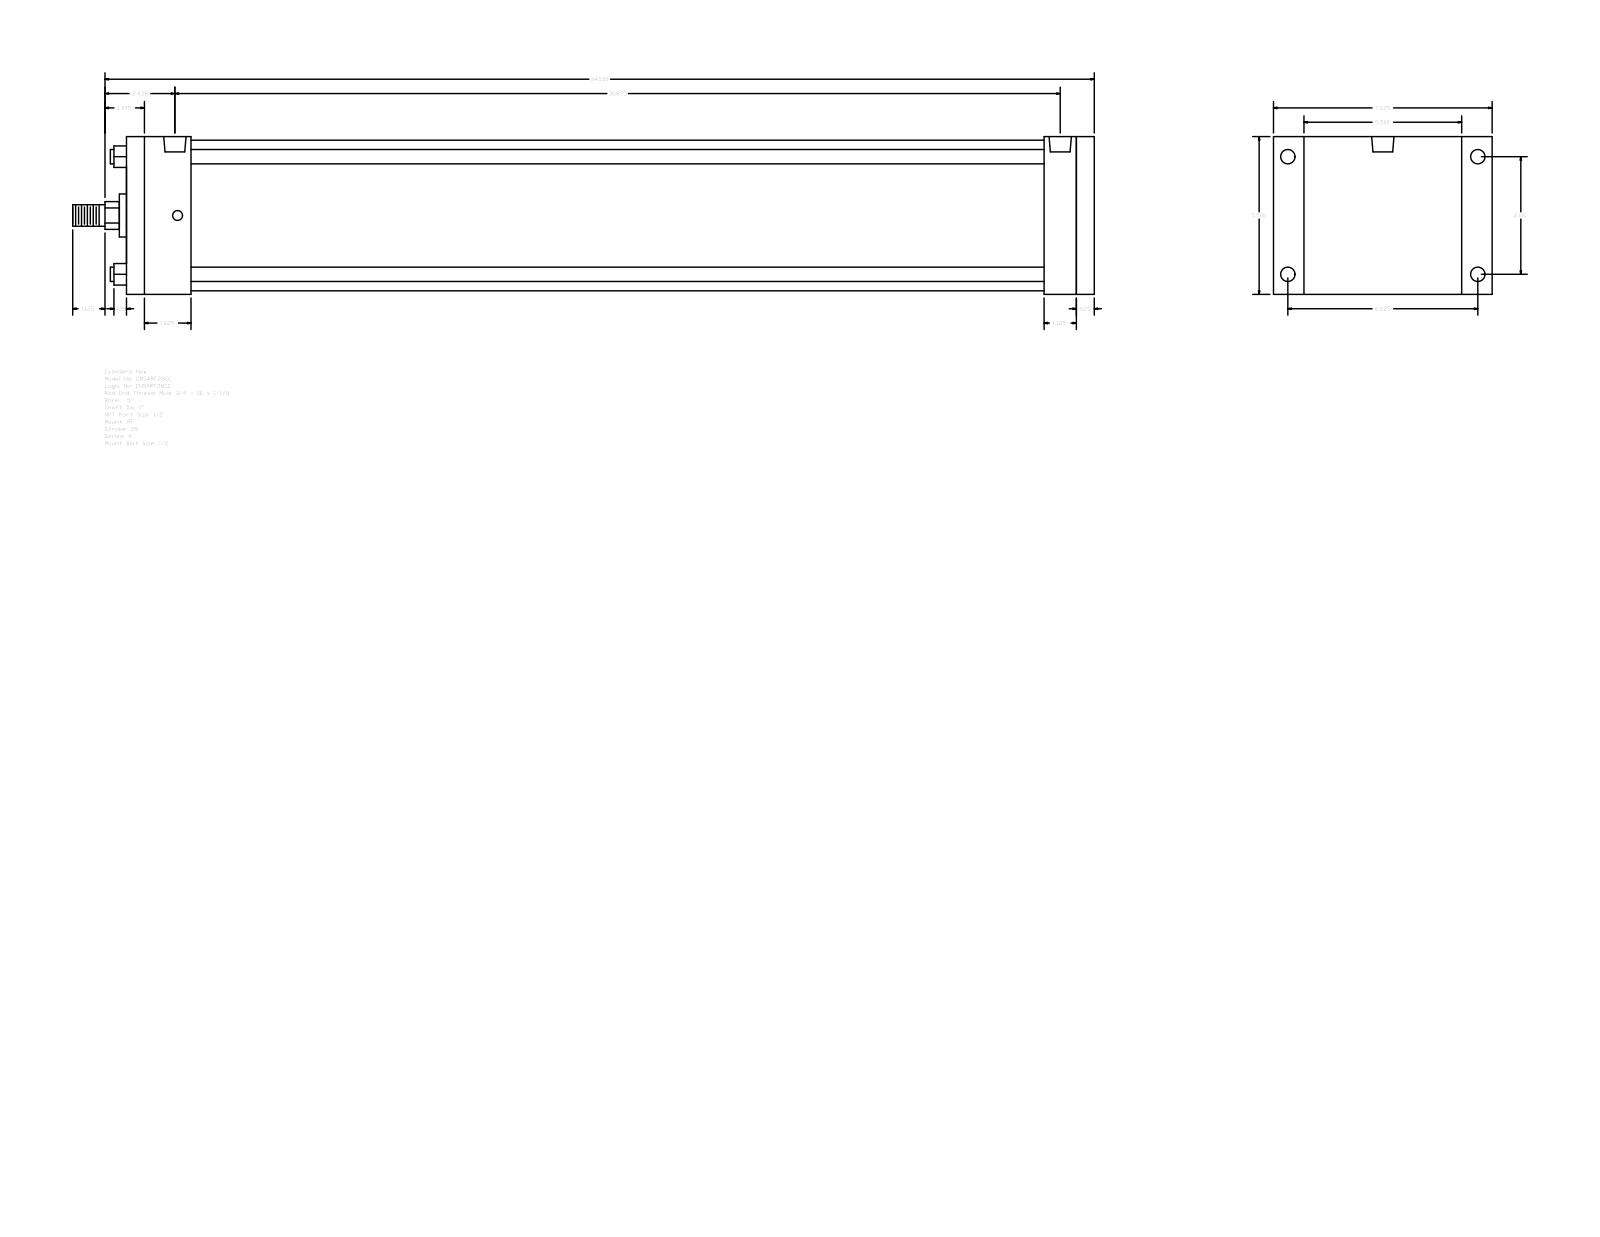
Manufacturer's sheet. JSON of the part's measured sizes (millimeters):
{"part_name": "A_RF__0500_1", "step_written_by": "GSSL Pune (CONFIG_CONTROL_DESIGN)", "units": "millimeters", "bodies": {"solids": 0, "faces": 92, "planar": 64, "cylindrical": 28, "other": 0}, "overall_size": [904.88, 193.68, 139.7], "round_holes": [[8.73, 4], [12.7, 4], [19.77, 2]], "round_bosses_or_shafts": [[12.7, 4], [133.35, 1], [38.1, 1], [25.4, 1], [19.05, 1]], "partial_cylinders_radius": [[12.29, 1]], "face_to_face_distances": [139.7, 857.25, 841.37, 15.88, 28.57, 57.15, 784.22, 800.1, 812.8, 755.65], "hole_center_spacings": [2.39, 104.14, 168.28, 197.9, 779.45, 781.84, 784.23]}
